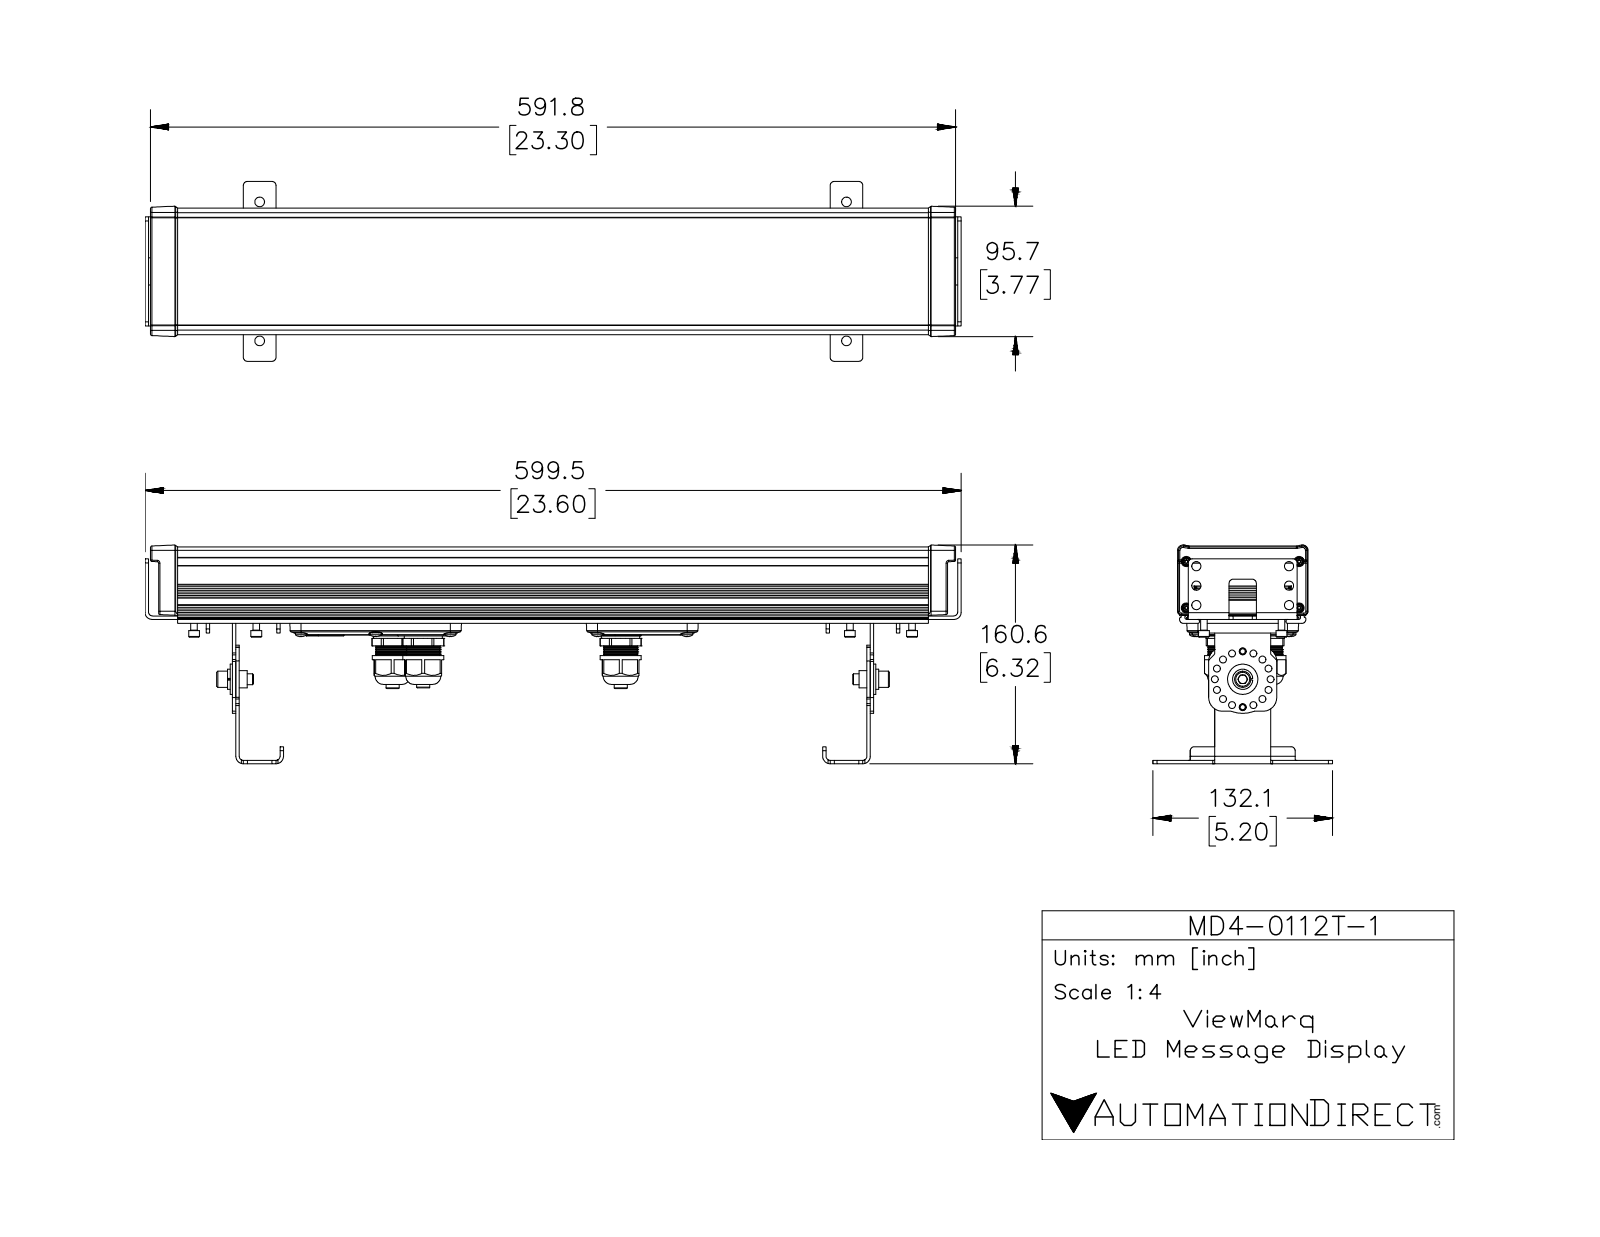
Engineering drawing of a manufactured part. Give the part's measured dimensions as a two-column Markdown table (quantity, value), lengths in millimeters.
| quantity | value |
| --- | --- |
| part name | MD4-0112T-1 |
| STEP written by | SolidWorks 2021 (AUTOMOTIVE_DESIGN) |
| units | millimeters |
| bodies | 51 solids, 5053 faces (1587 planar, 2005 cylindrical, 1461 other) |
| overall size | 599.5 × 160.7 × 132.1 |
| volume | 953 100 mm³ |
| surface area | 736 800 mm² |
| round holes (diameter × count) | 5.1 × 24, 7.1 × 12, 3.5 × 10, 4.7 × 10, 4.8 × 6, 6.8 × 6, 3 × 4, 3.7 × 4, 4 × 4, 13.5 × 3, 15.3 × 3, 20.4 × 3 |
| round bosses / shafts (diameter × count) | 8 × 9, 4.8 × 4, 30 × 3, 25 × 3, 21.3 × 3, 9.6 × 3, 7.1 × 3, 5.5 × 3 |
| partial cylindrical surfaces (radius × count) | 0.5 × 294, 0.5 × 248, 3 × 62, 0.3 × 52, 1 × 50, 0.3 × 38, 0.6 × 36, 1.1 × 30 |
| main face-to-face distances | 3, 2, 41.1, 43.1, 44.1, 46.1, 2.5, 6, 1.5, 4.5 |
| hole center spacings | 8, 34.1, 37.9, 20.5, 29, 15.7, 22.8, 40.2 |
